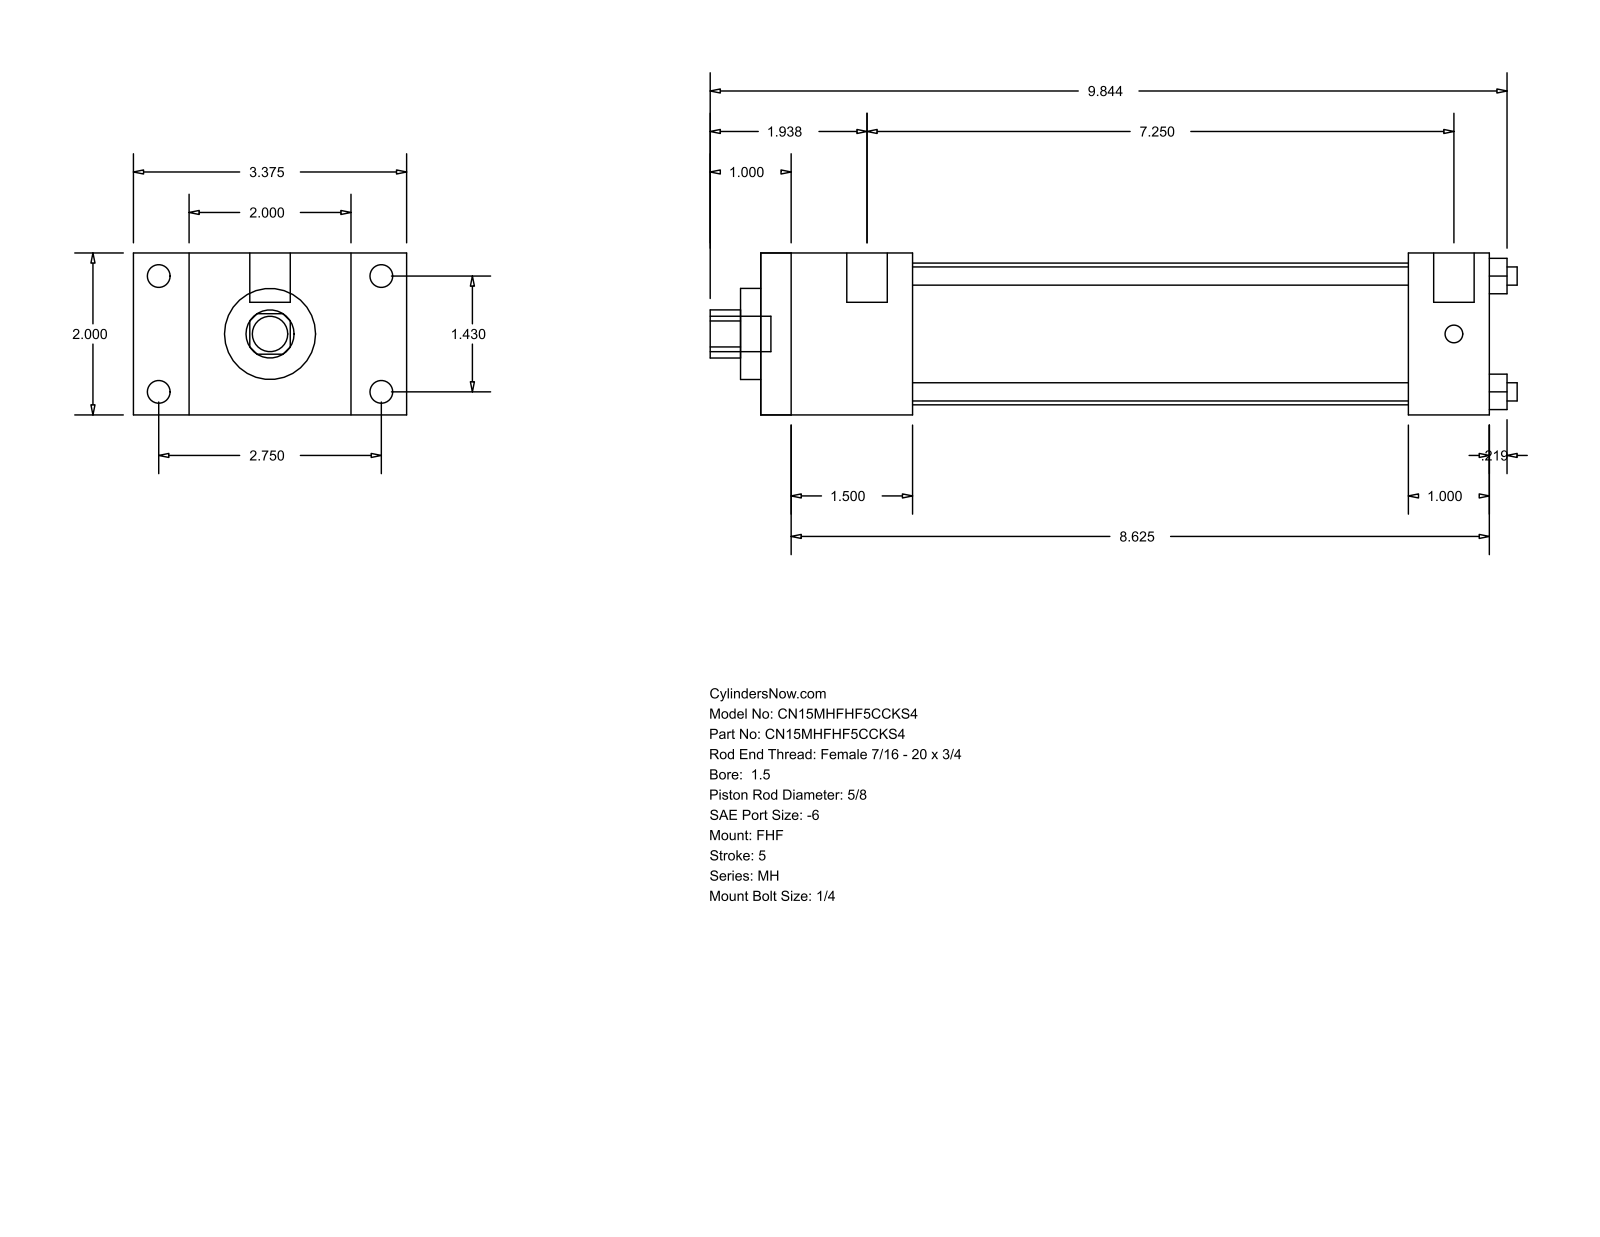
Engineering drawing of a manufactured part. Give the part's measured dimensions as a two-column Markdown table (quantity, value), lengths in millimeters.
| quantity | value |
| --- | --- |
| part name | MH_FHF__0150_0.625 |
| STEP written by | GSSL Pune (CONFIG_CONTROL_DESIGN) |
| units | millimeters |
| bodies | 0 solids, 88 faces (60 planar, 28 cylindrical, 0 other) |
| overall size | 253.21 × 85.72 × 50.8 |
| round holes (diameter × count) | 5.71 × 4, 15.88 × 1, 28.57 × 1, 44.45 × 1 |
| round bosses / shafts (diameter × count) | 7.14 × 4, 5.56 × 4, 12.7 × 2, 11.11 × 1 |
| partial cylindrical surfaces (radius × count) | 7.54 × 1 |
| main face-to-face distances | 50.8, 17.46, 68.26, 47.62, 85.72, 228.59, 180.97, 203.19, 155.57, 25.4 |
| hole center spacings | 25.68, 36.32, 51.36 |
